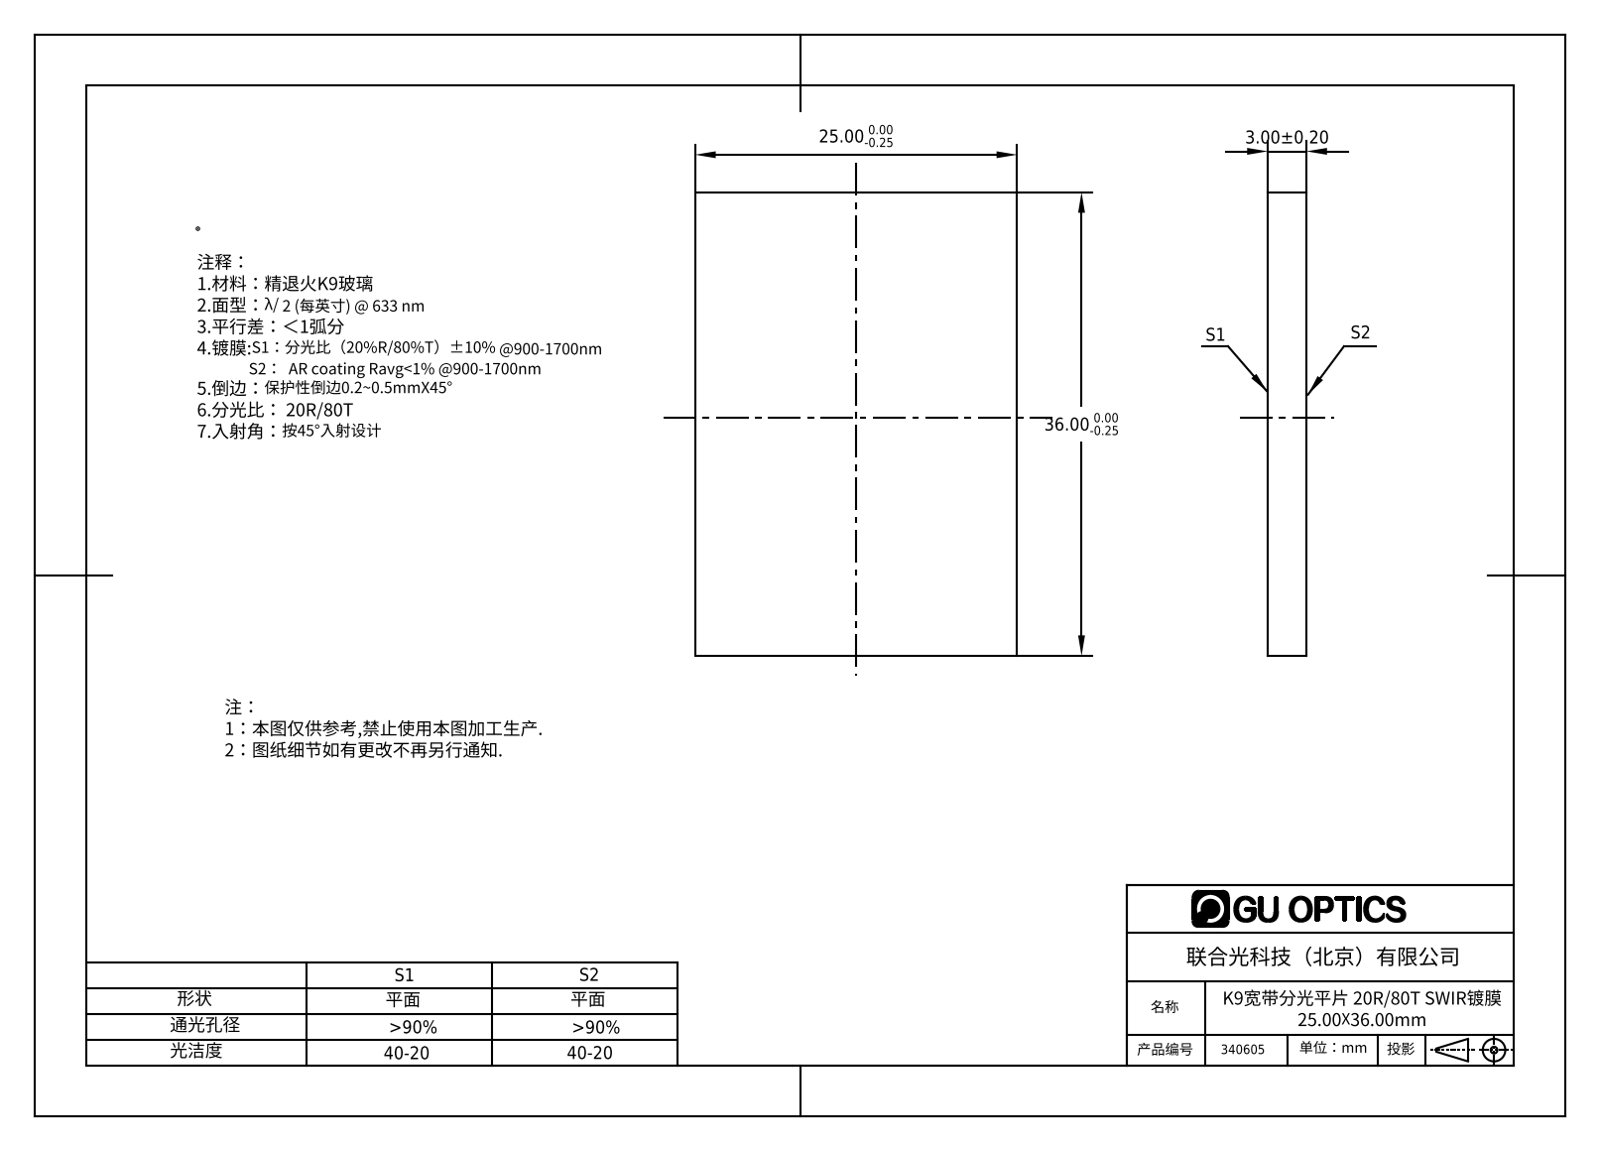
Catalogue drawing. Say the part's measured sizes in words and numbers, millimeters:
The part is named "340521". Its 3-D file was written by "SolidWorks 2016 (CONFIG_CONTROL_DESIGN)". It is 1 solid with 6 faces: 6 planar, 0 cylindrical and 0 other. Overall it measures 36 by 25 by 3 millimeters. Its volume is 2 700 cubic millimeters and its surface area 2 166 square millimeters. The main face-to-face distances are 3, 25, 36.
